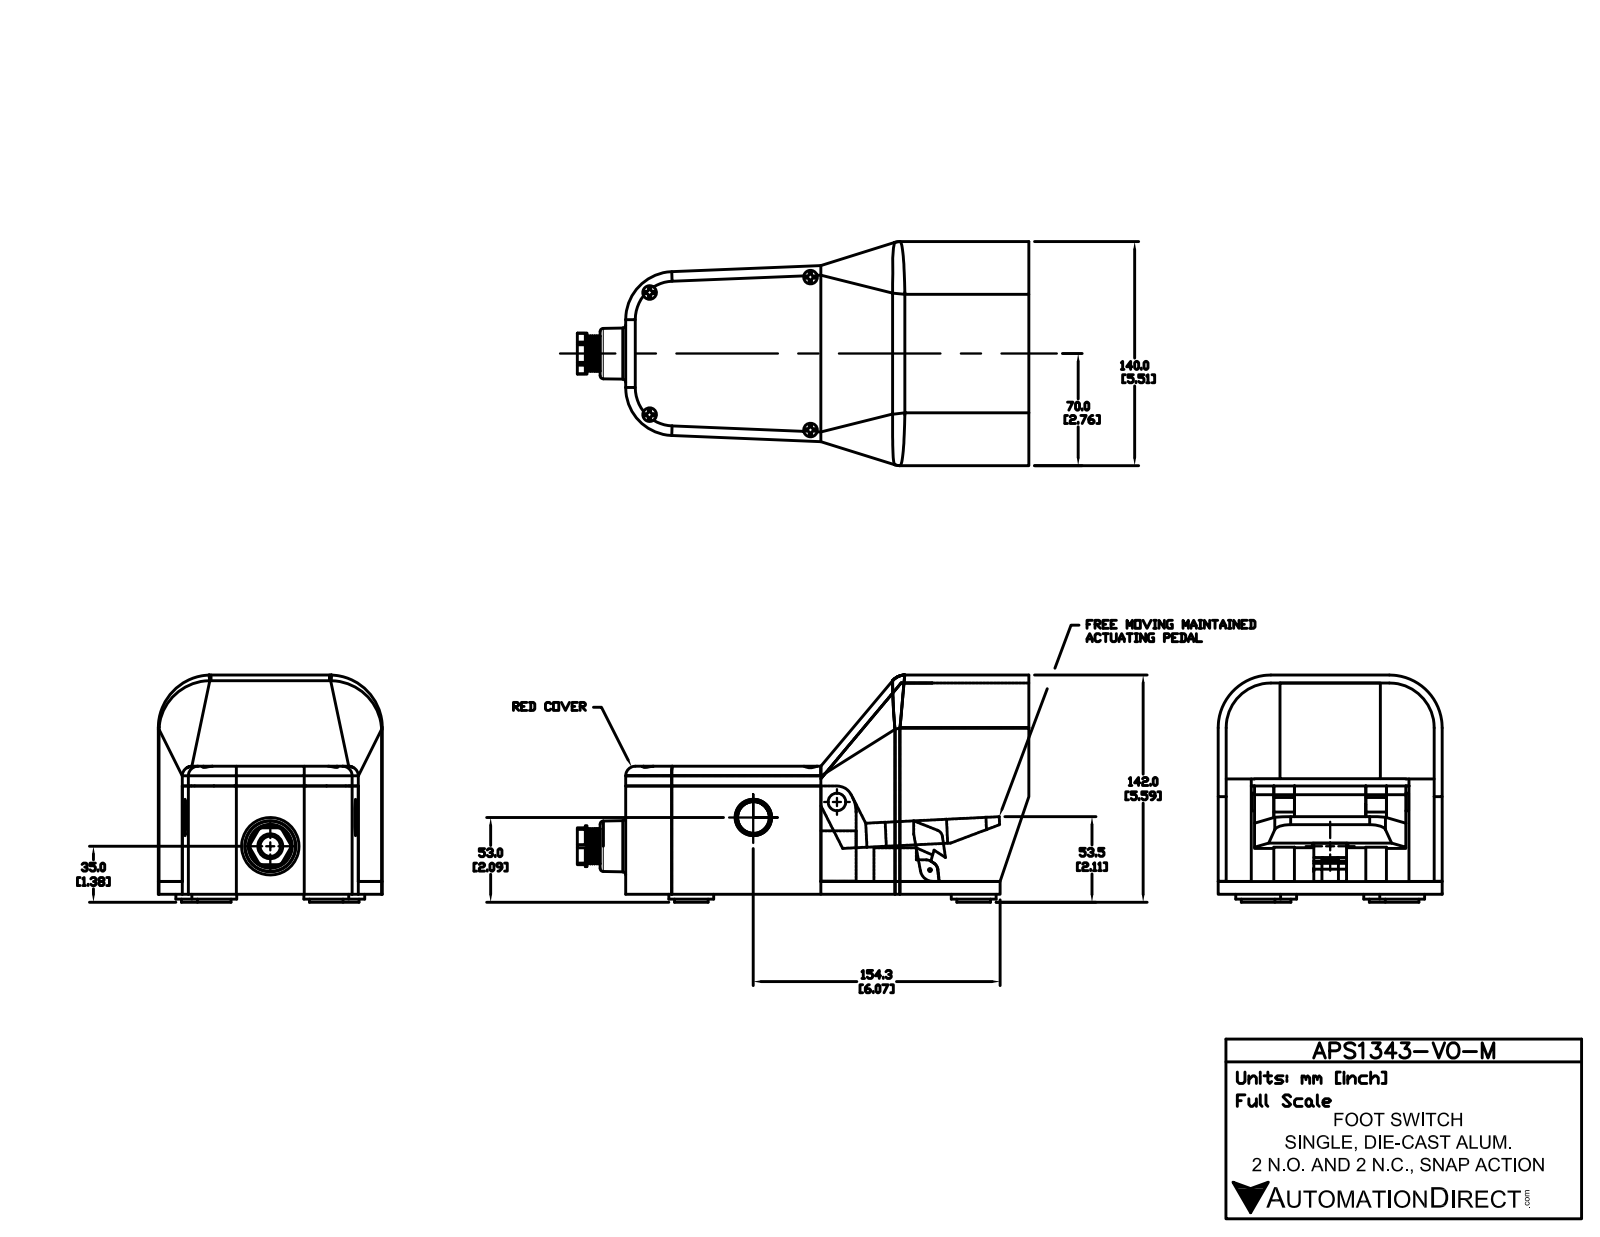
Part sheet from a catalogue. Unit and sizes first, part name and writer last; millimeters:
Units: millimetres
Overall size (bounding box): 282.25 × 142 × 140
Round holes (diameter × count): ⌀8.5 ×4, ⌀22.75 ×2, ⌀12.65 ×1, ⌀15.6 ×1
Round bosses / shafts (diameter × count): ⌀28 ×4, ⌀21 ×4, ⌀19.87 ×2, ⌀25.5 ×1, ⌀22 ×1, ⌀11 ×1, ⌀1.9 ×1
Partial cylindrical surfaces — rounded edges, fillets, slot ends (radius × count): R1 ×16, R10 ×6, R5 ×4, R5.99 ×3, R28 ×2, R30 ×2, R33 ×2, R8 ×1
Main face-to-face distances: 5, 135, 8, 59.64, 67.67, 59.67, 67.64, 140, 72, 80
Hole centre spacings: 101, 132.24, 76.3, 95.5
Volume: 1 555 000 mm³ · Surface area: 273 234 mm²
Bodies: 19 solids, 400 faces (242 planar, 102 cylindrical, 56 other)
Part name (STEP PRODUCT): APS1343-V0-M
STEP written by: SolidWorks 2015 (AUTOMOTIVE_DESIGN)
